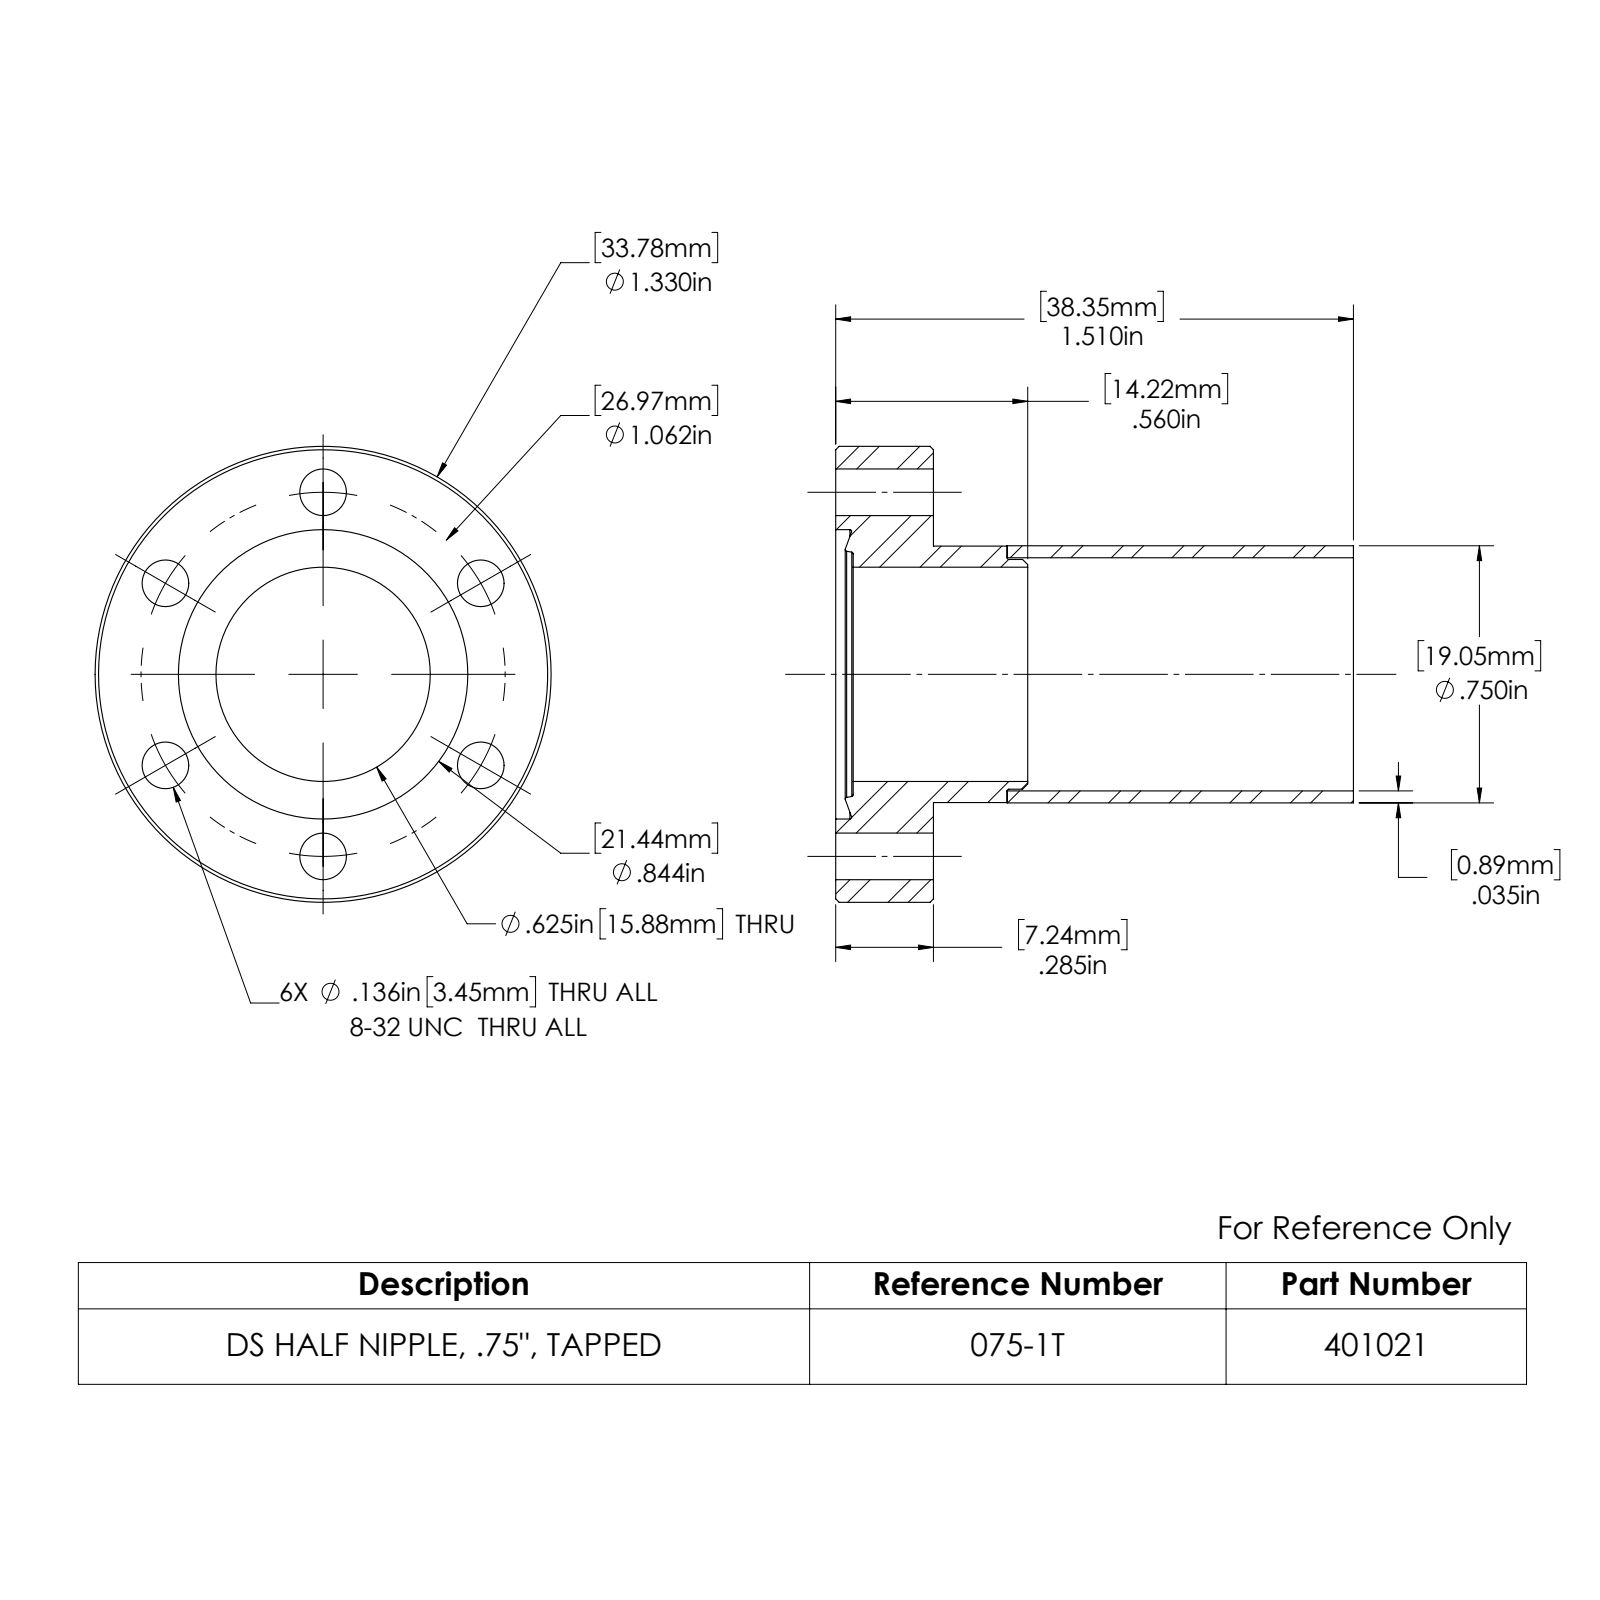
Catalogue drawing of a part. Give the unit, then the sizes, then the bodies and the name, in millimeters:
Units: millimetres
Overall size (bounding box): 38.4 × 33.8 × 33.8
Round holes (diameter × count): ⌀3.5 ×6, ⌀15.9 ×1, ⌀17.3 ×1, ⌀21.4 ×1
Round bosses / shafts (diameter × count): ⌀33.8 ×1, ⌀19.1 ×1, ⌀19 ×1, ⌀17 ×1
Main face-to-face distances: 7.2, 12.7, 5.5, 1.3, 5.9, 11.4, 38.4, 37.1, 31.1, 25.7
Hole centre spacings: 13.5, 23.4, 13.5, 27, 27
Volume: 6 280 mm³ · Surface area: 6 665 mm²
Bodies: 2 solids, 51 faces (7 planar, 26 cylindrical, 18 other)
Part name (STEP PRODUCT): 940100; 401021; 130004
STEP written by: SolidWorks 2022 (AUTOMOTIVE_DESIGN)
